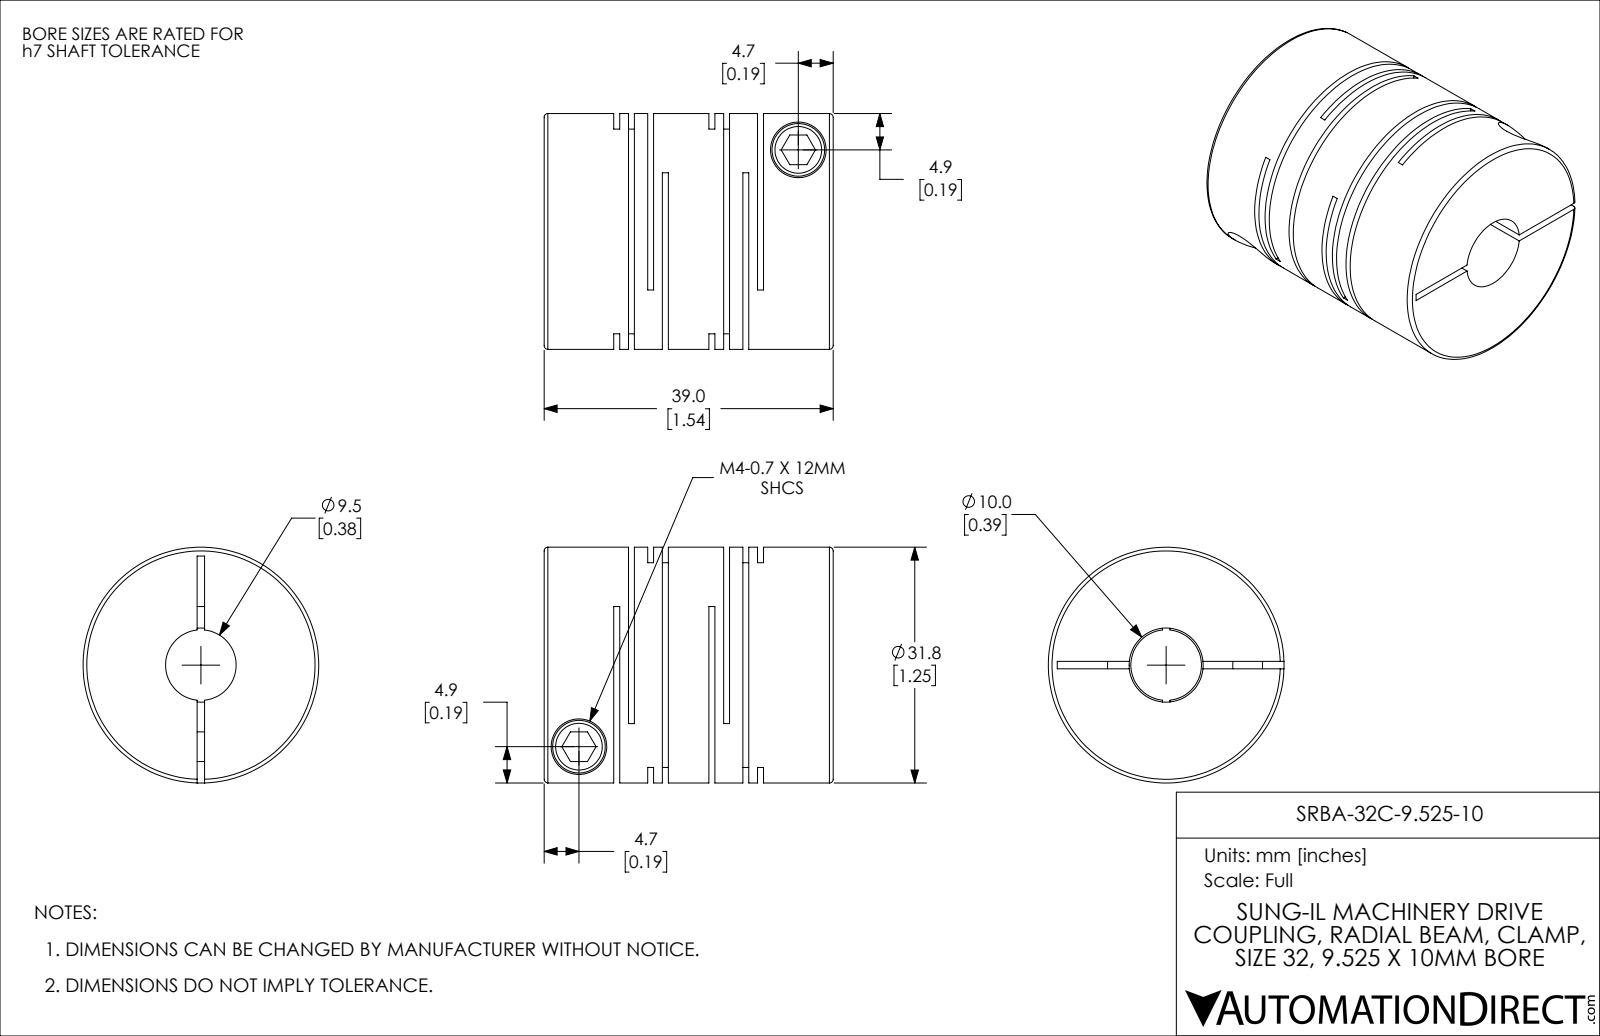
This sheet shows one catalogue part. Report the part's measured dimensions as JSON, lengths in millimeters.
{"part_name": "SRBA-32C-9.525-10", "step_written_by": "SolidWorks 2021 (CONFIG_CONTROL_DESIGN)", "units": "millimeters", "bodies": {"solids": 1, "faces": 114, "planar": 60, "cylindrical": 42, "other": 12}, "overall_size": [39, 31.8, 31.8], "volume_mm3": 23514, "surface_area_mm2": 16217, "round_holes": [[4, 2], [7.5, 2], [9.53, 1], [10, 1]], "round_bosses_or_shafts": [[7.1, 2], [31.8, 1]], "face_to_face_distances": [0.8, 12.84, 1.98, 4.58, 12.04, 1.18, 10.86, 3.78, 8.26, 2.6]}
